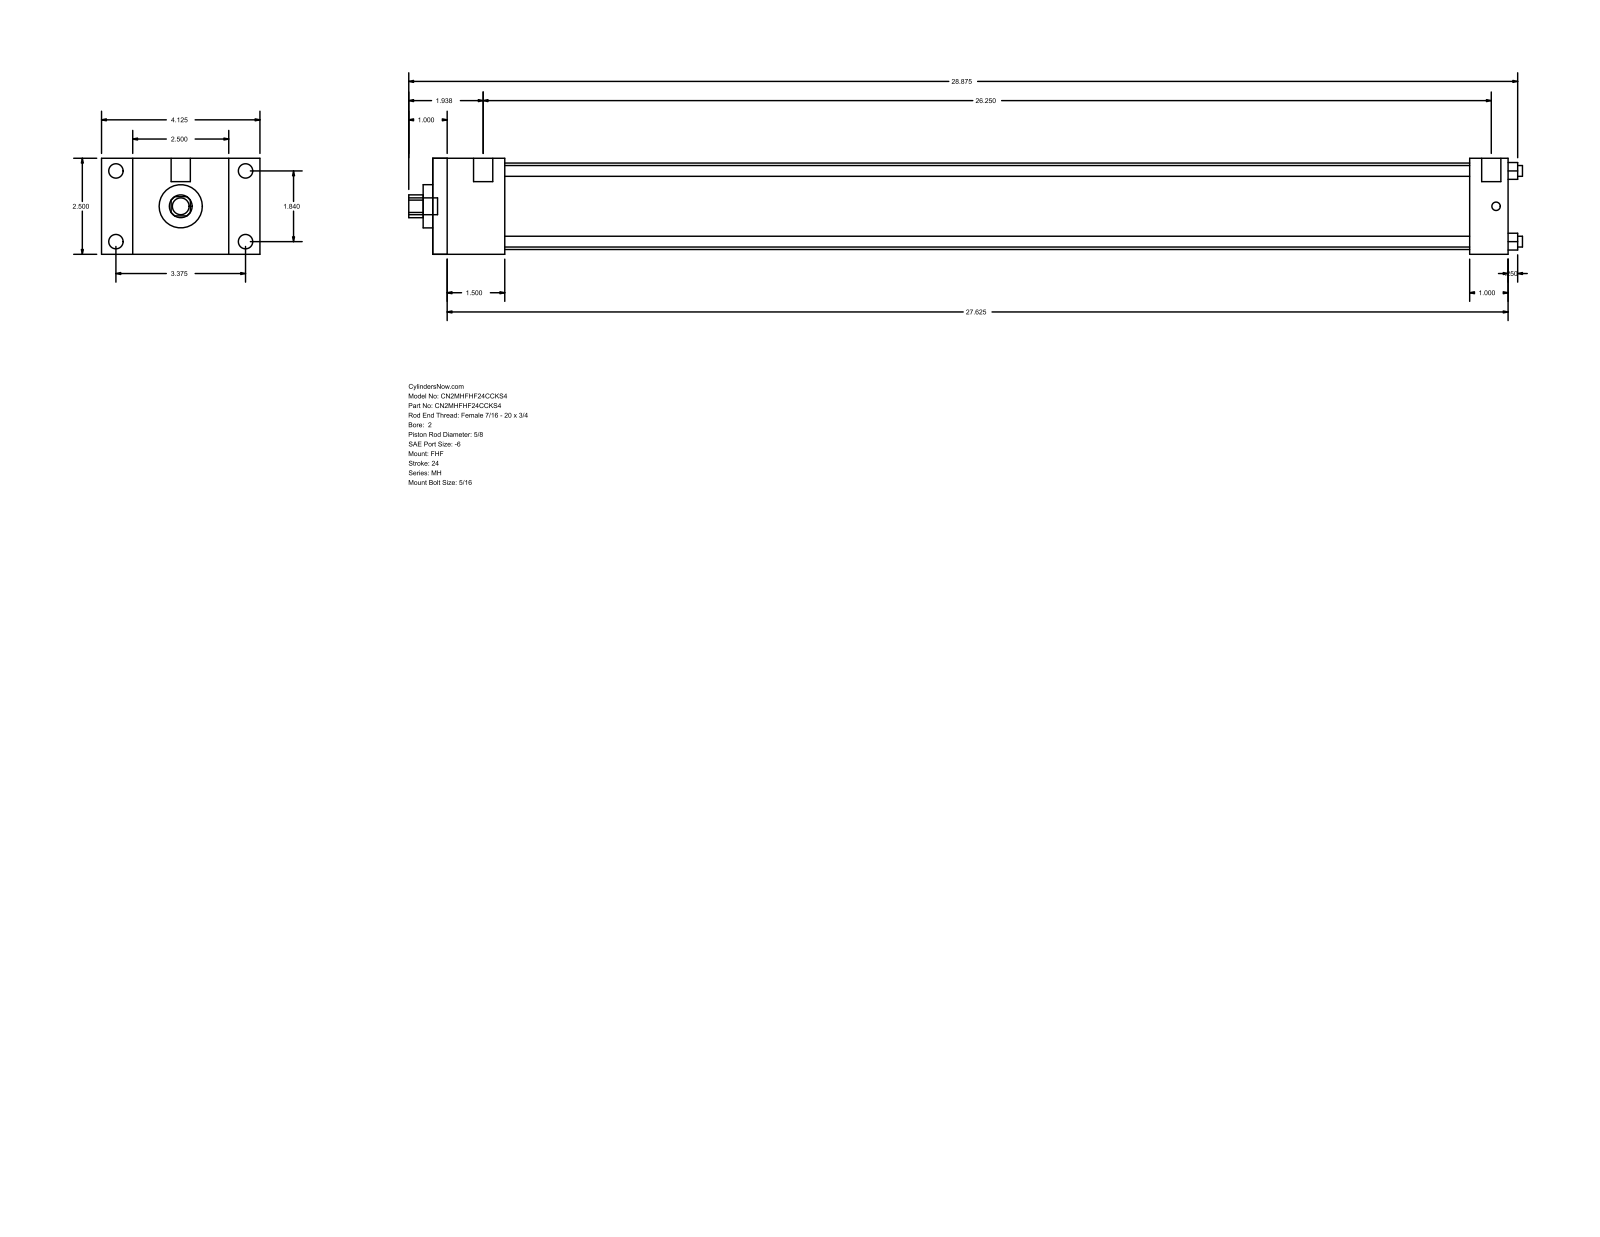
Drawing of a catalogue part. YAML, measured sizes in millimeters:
part_name: "MH_FHF__0200_0.625"
step_written_by: "GSSL Pune (CONFIG_CONTROL_DESIGN)"
units: millimeters
bodies: {solids: 0, faces: 88, planar: 60, cylindrical: 28, other: 0}
overall_size: [736.6, 104.78, 63.5]
round_holes:
  - {diameter: 7.14, count: 4}
  - {diameter: 15.88, count: 1}
  - {diameter: 28.57, count: 1}
  - {diameter: 57.15, count: 1}
round_bosses_or_shafts:
  - {diameter: 9.53, count: 4}
  - {diameter: 5.56, count: 4}
  - {diameter: 12.7, count: 2}
  - {diameter: 11.11, count: 1}
partial_cylinders:
  - {radius: 7.54, count: 1}
face_to_face_distances: [63.5, 47.62, 711.2, 663.58, 20.64, 84.14, 104.78, 685.79, 638.17, 25.41]
hole_center_spacings: [33.05, 46.74, 66.1]
